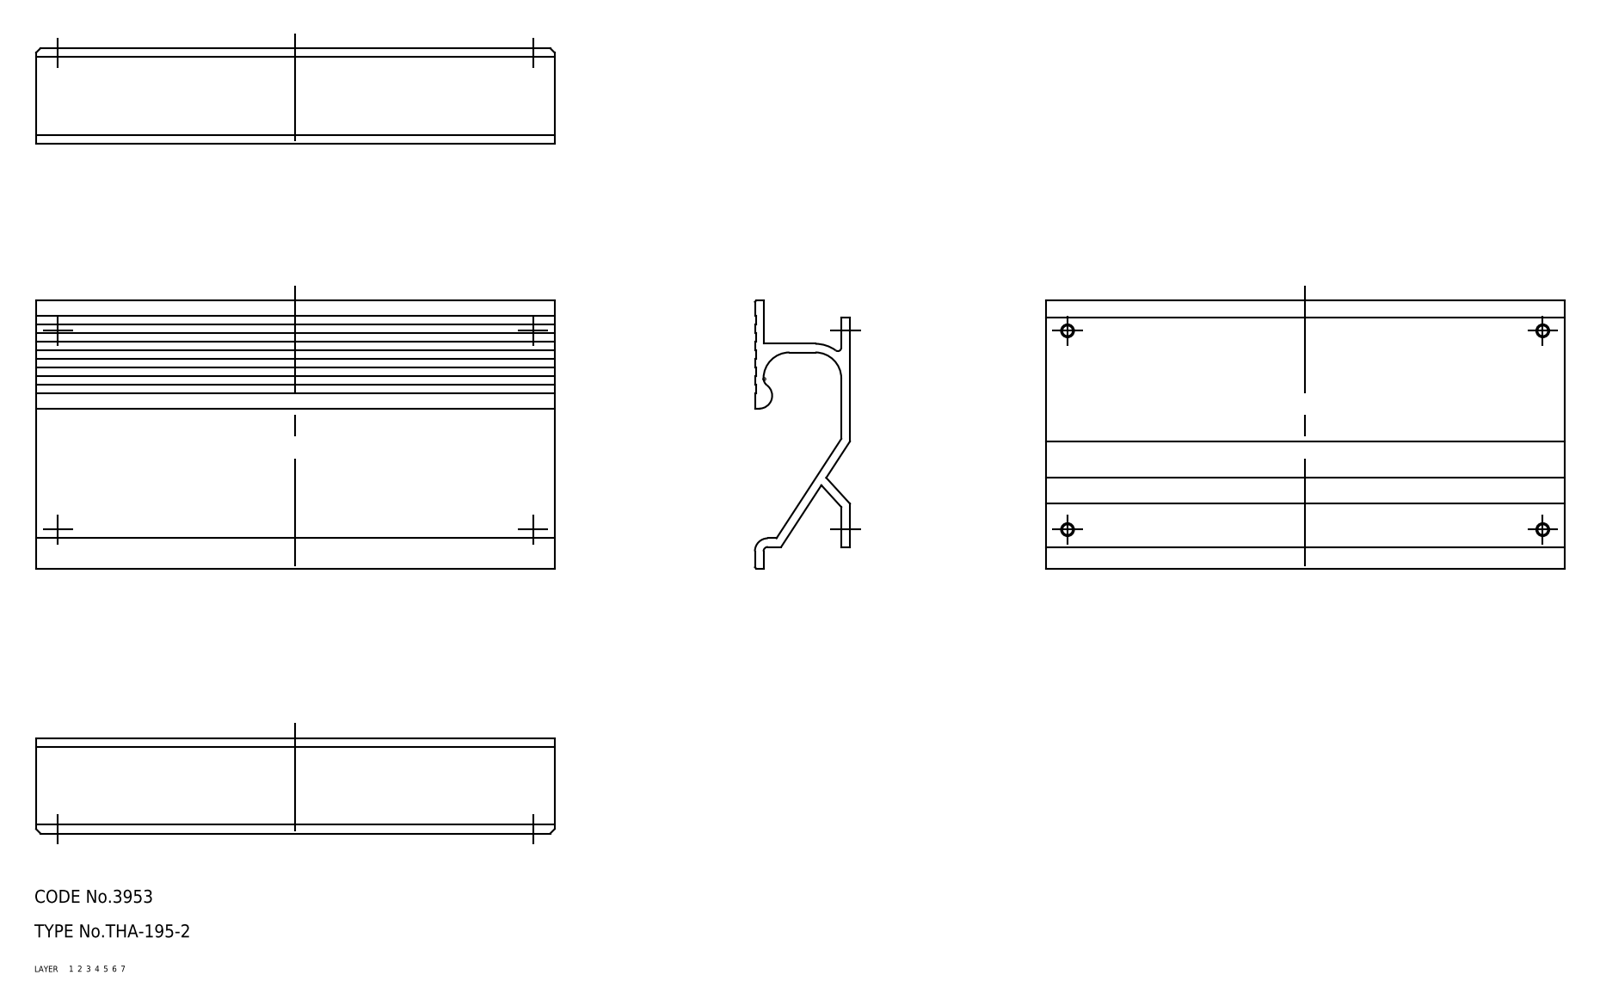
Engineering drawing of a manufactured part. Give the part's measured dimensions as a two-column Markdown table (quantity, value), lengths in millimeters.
| quantity | value |
| --- | --- |
| part name | pull |
| STEP written by | CADfix (AUTOMOTIVE_DESIGN) |
| units | millimeters |
| bodies | 1 solid, 67 faces (0 planar, 0 cylindrical, 67 other) |
| overall size | 120 × 62 × 22 |
| volume | 32 202 mm³ |
| surface area | 31 377 mm² |
